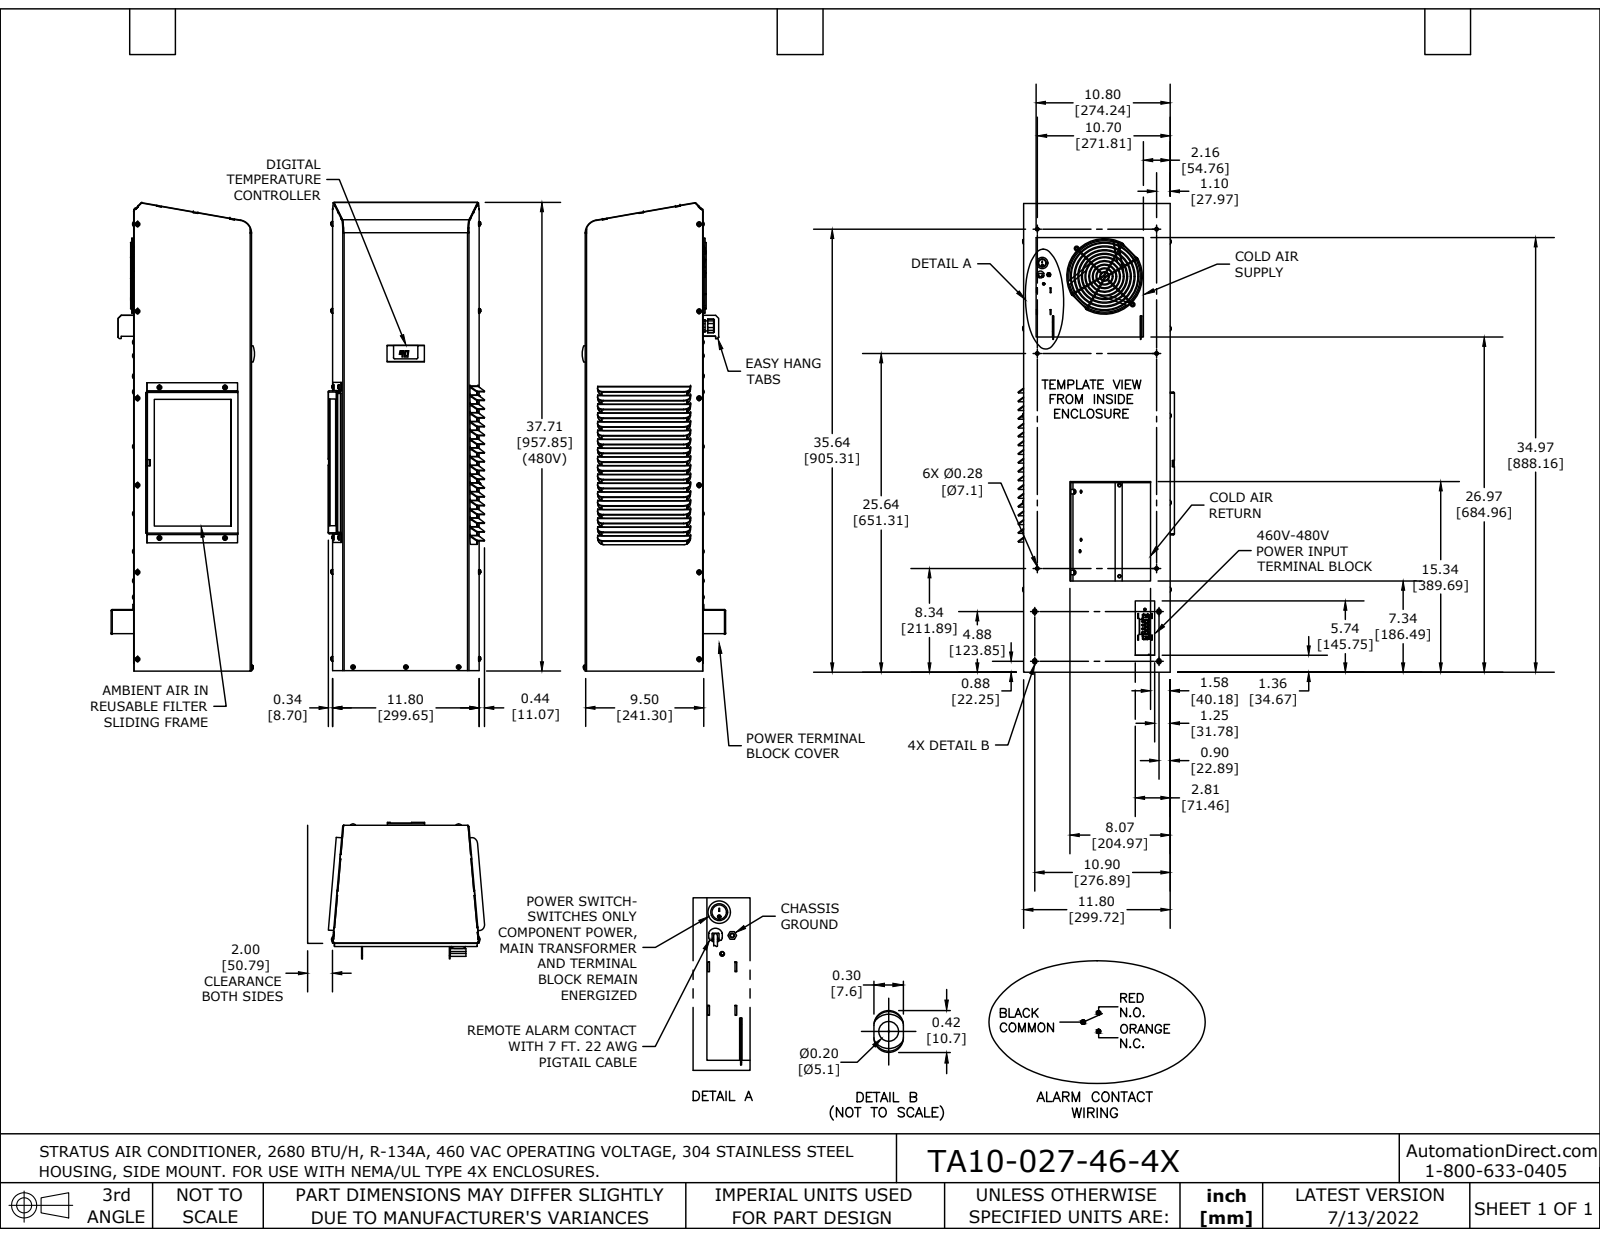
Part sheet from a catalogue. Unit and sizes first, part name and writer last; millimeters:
Units: millimetres
Overall size (bounding box): 813.4 × 319.4 × 293.3
Round holes (diameter × count): ⌀4 ×11, ⌀5.2 ×5, ⌀152.4 ×1
Round bosses / shafts (diameter × count): ⌀4.8 ×7, ⌀6.3 ×2, ⌀154.2 ×1, ⌀23 ×1, ⌀2.2 ×1
Partial cylindrical surfaces — rounded edges, fillets, slot ends (radius × count): R0.4 ×45, R0.3 ×42, R12.7 ×36, R12.9 ×36, R2.5 ×28, R1.5 ×21, R2.9 ×21, R0.8 ×13
Main face-to-face distances: 1.5, 239.6, 238.2, 1.5, 241.1, 2.3, 6.4, 7.8, 246, 247.5
Hole centre spacings: 177.8, 355.6, 533.4, 44, 134.6, 166.8, 276.1, 307.8
Volume: 2 206 000 mm³ · Surface area: 2 062 000 mm²
Bodies: 1 solid, 1569 faces (956 planar, 463 cylindrical, 150 other)
Part name (STEP PRODUCT): TA10-027-46-4X
STEP written by: SolidWorks 2021 (AUTOMOTIVE_DESIGN)
